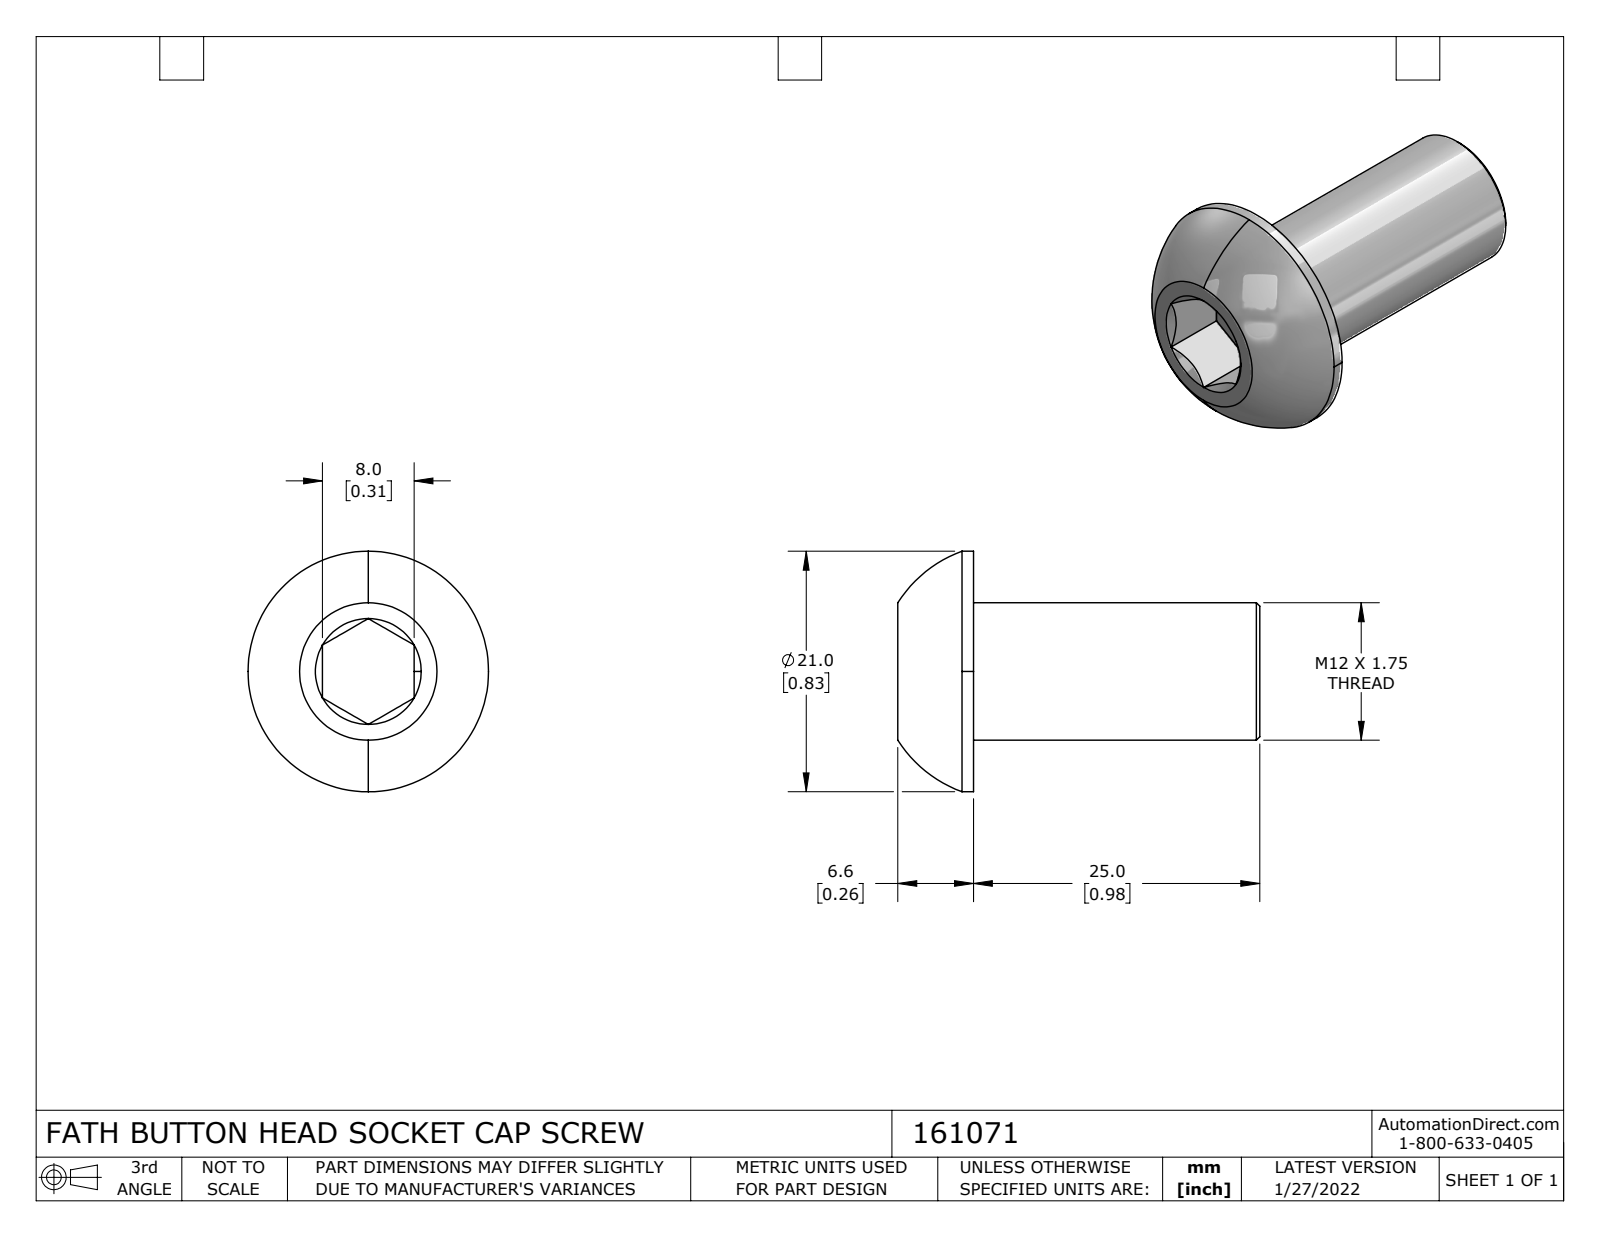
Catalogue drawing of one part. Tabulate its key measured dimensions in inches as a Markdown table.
| quantity | value |
| --- | --- |
| part name | 161071 |
| STEP written by | SolidWorks 2021 (CONFIG_CONTROL_DESIGN) |
| units | inches |
| bodies | 1 solid, 25 faces (10 planar, 4 cylindrical, 11 other) |
| overall size | 1.244 × 0.827 × 0.827 |
| volume | 0.259 in³ |
| surface area | 3.105 in² |
| round bosses / shafts (diameter × count) | 0.827 × 1, 0.472 × 1 |
| main face-to-face distances | 0.984, 0.315, 1.024, 0.039, 1.244, 0.26, 0.22 |
